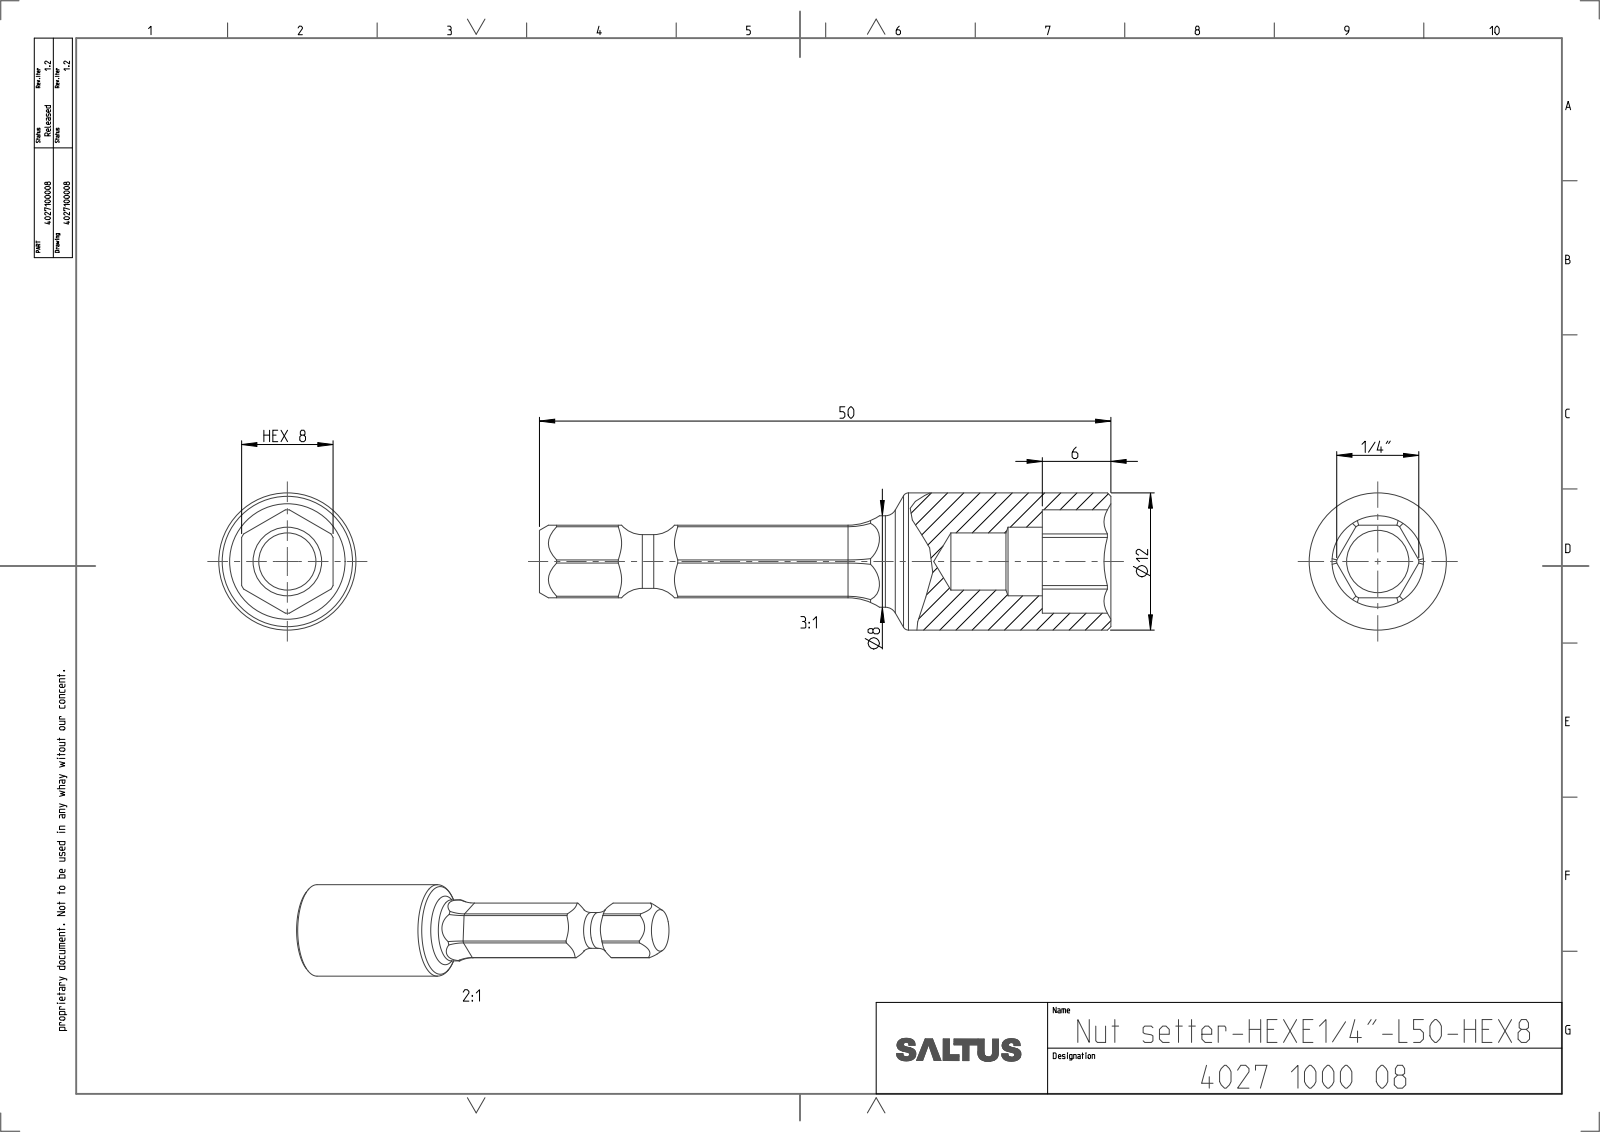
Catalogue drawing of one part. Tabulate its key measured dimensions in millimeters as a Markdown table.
| quantity | value |
| --- | --- |
| part name | 4027100008 |
| STEP written by | CREO PARAMETRIC BY PTC INC, 2022414 (CONFIG_CONTROL_DESIGN) |
| units | millimeters |
| bodies | 1 solid, 81 faces (21 planar, 34 cylindrical, 26 other) |
| overall size | 50 × 12 × 12 |
| volume | 2 630 mm³ |
| surface area | 1 833 mm² |
| round holes (diameter × count) | 5 × 1, 6 × 1 |
| round bosses / shafts (diameter × count) | 12 × 1, 8 × 1, 4.7 × 1 |
| partial cylindrical surfaces (radius × count) | 5 × 6, 3.59 × 1, 4.52 × 1 |
| main face-to-face distances | 6.34, 6.36, 8, 44, 50, 6 |
